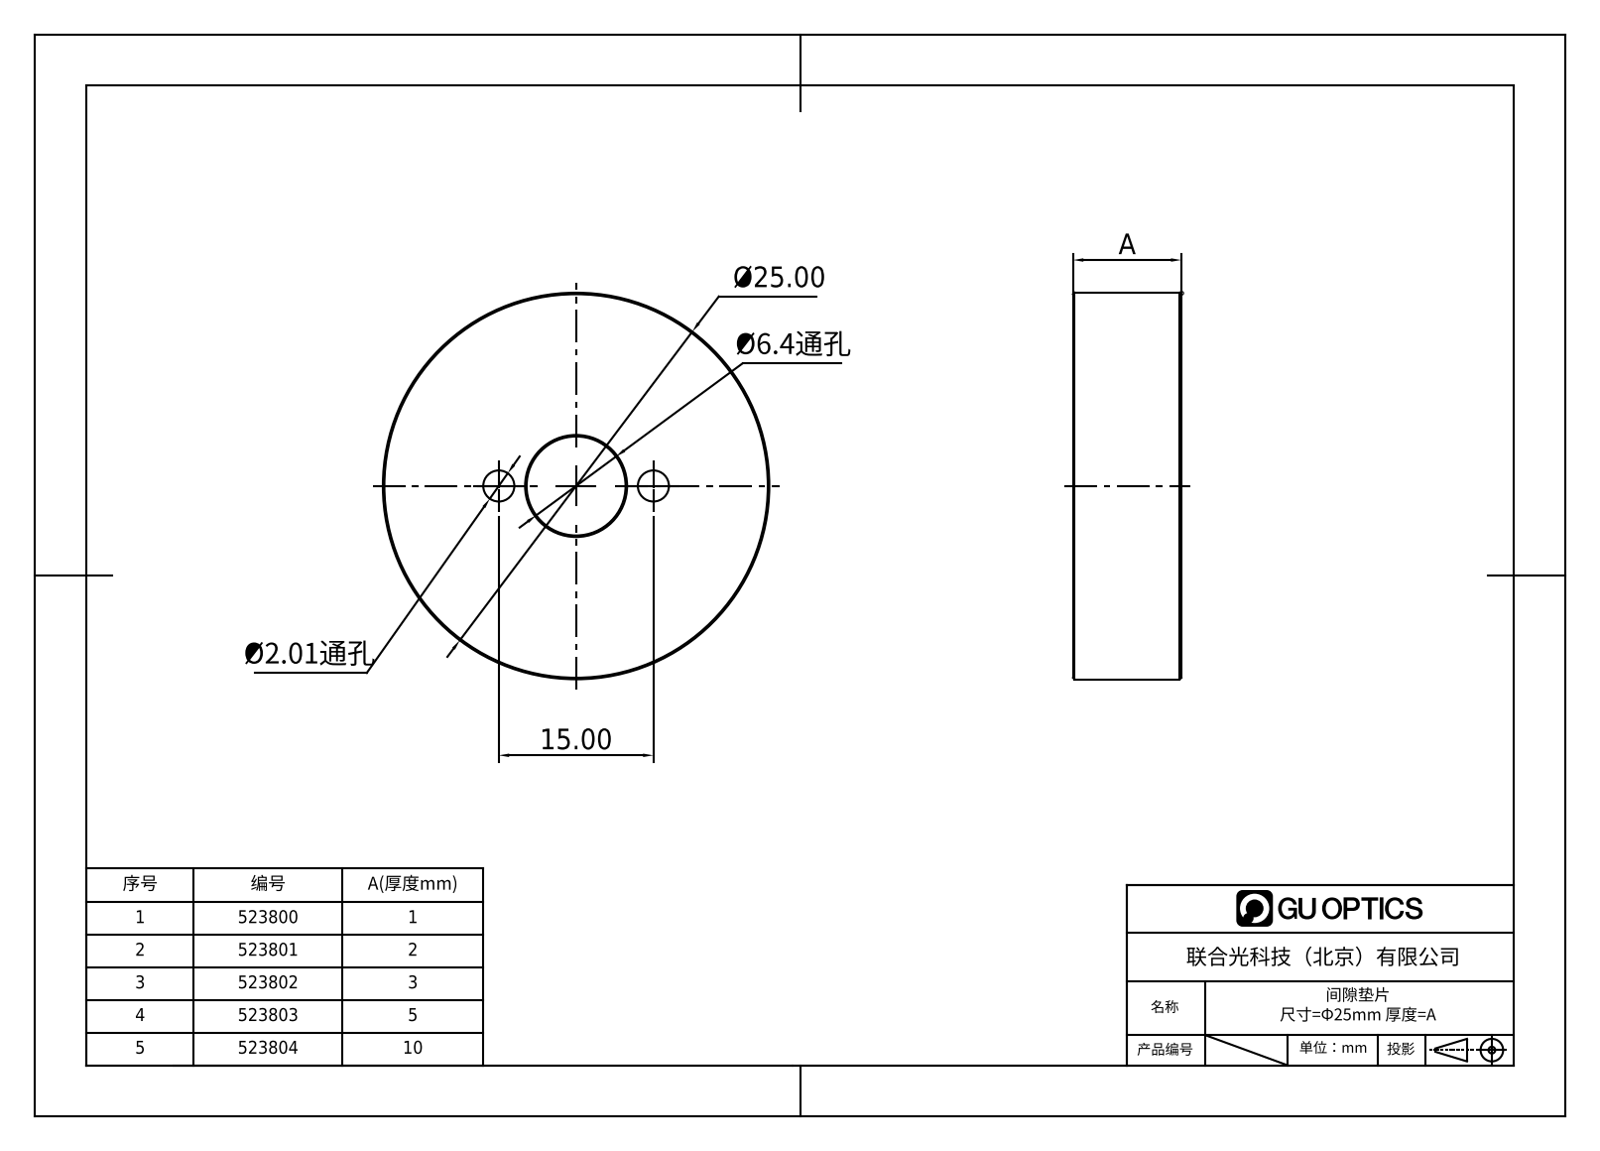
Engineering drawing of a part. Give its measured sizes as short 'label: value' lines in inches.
name: 523802
written by: SolidWorks 2020 (CONFIG_CONTROL_DESIGN)
unit: in
bodies: 1 solid, 14 faces (2 planar, 4 cylindrical, 8 other)
size: 0.984 × 0.984 × 0.118
volume: 0.083 in³; area: 1.88 in²
holes: 2× ⌀0.079, 1× ⌀0.252
bosses: 1× ⌀0.984
face distances: 0.118
hole spacings: 0.197, 0.394
